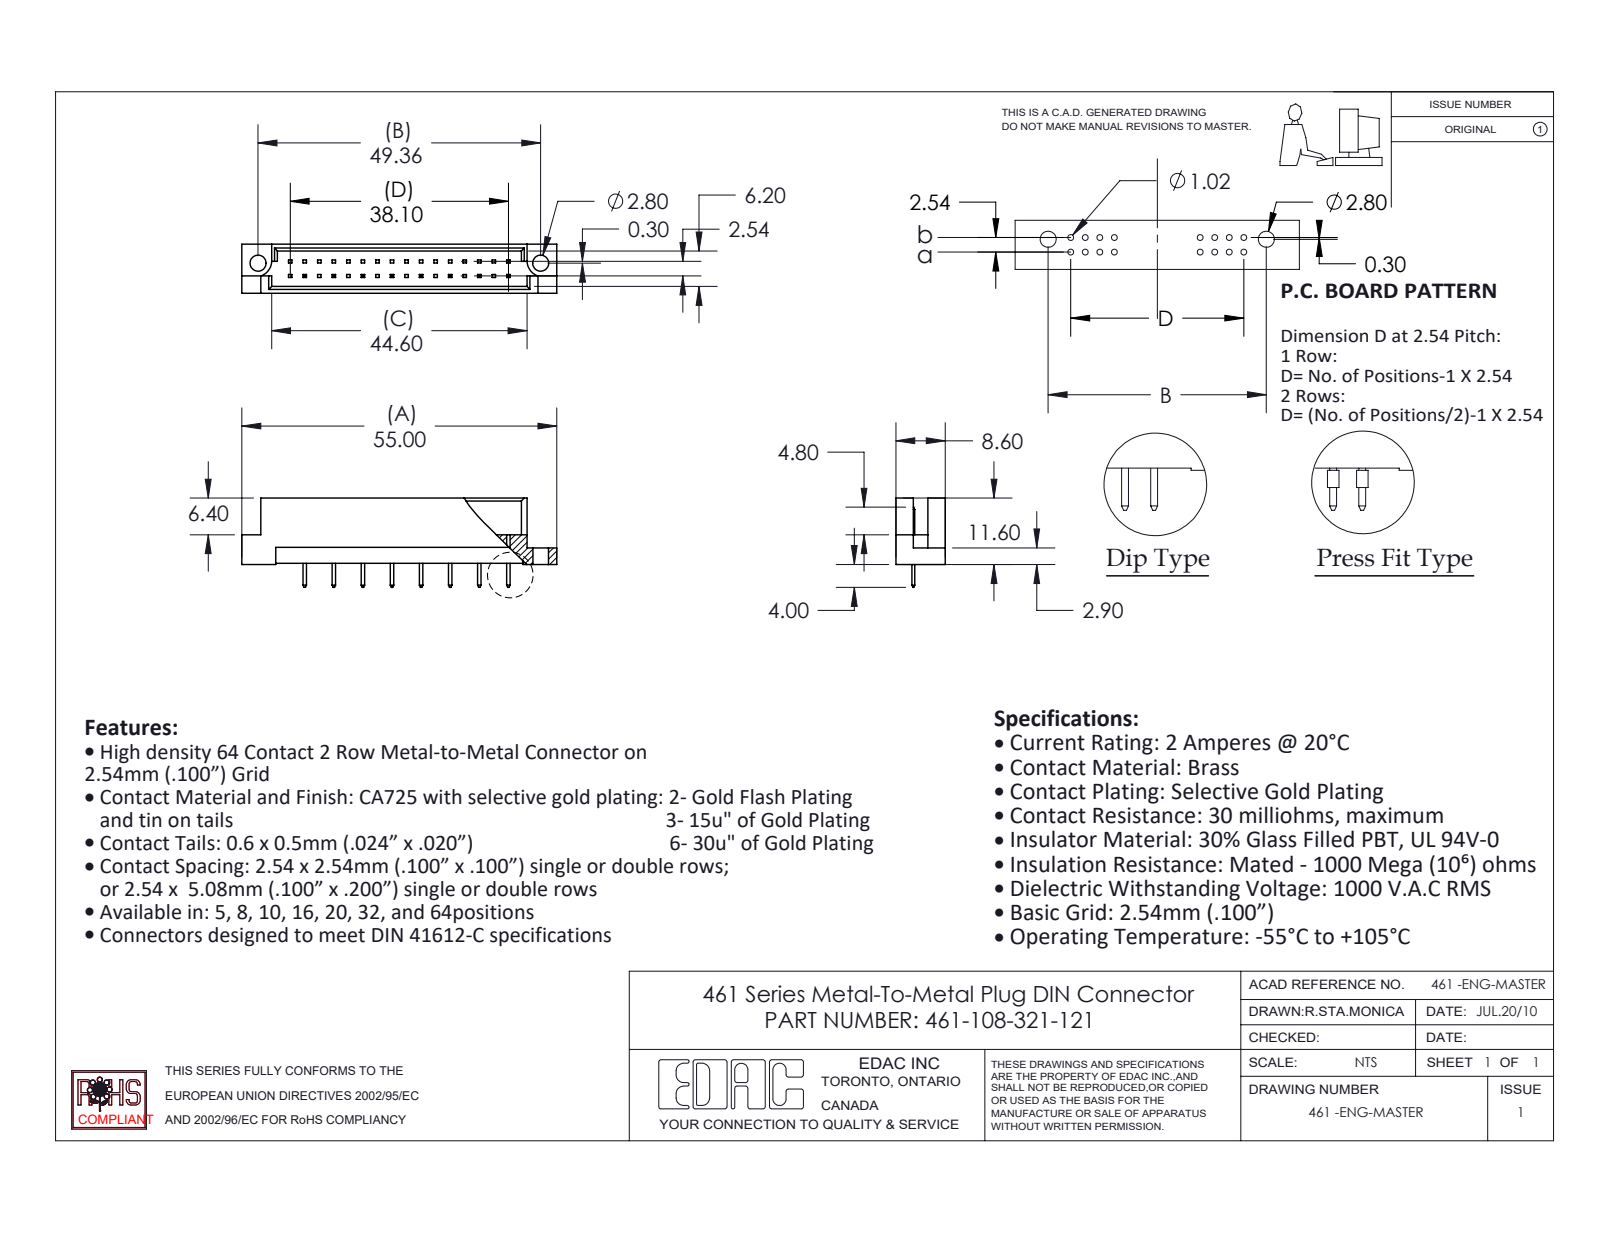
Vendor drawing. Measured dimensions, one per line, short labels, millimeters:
name: 461 Part_32; 461-290_21; 461-108-321-121
written by: SolidWorks 2020 (CONFIG_CONTROL_DESIGN)
unit: mm
bodies: 9 solids, 288 faces (282 planar, 6 cylindrical, 0 other)
size: 55 × 15.6 × 8.6
volume: 2 687 mm³; area: 3 491 mm²
holes: 2× ⌀2.8
rounds: 2× R2.8
face distances: 1.2, 7.4, 8.6, 6.2, 5, 2.78, 5.82, 1.58, 4.62, 3.28
hole spacings: 49.36
